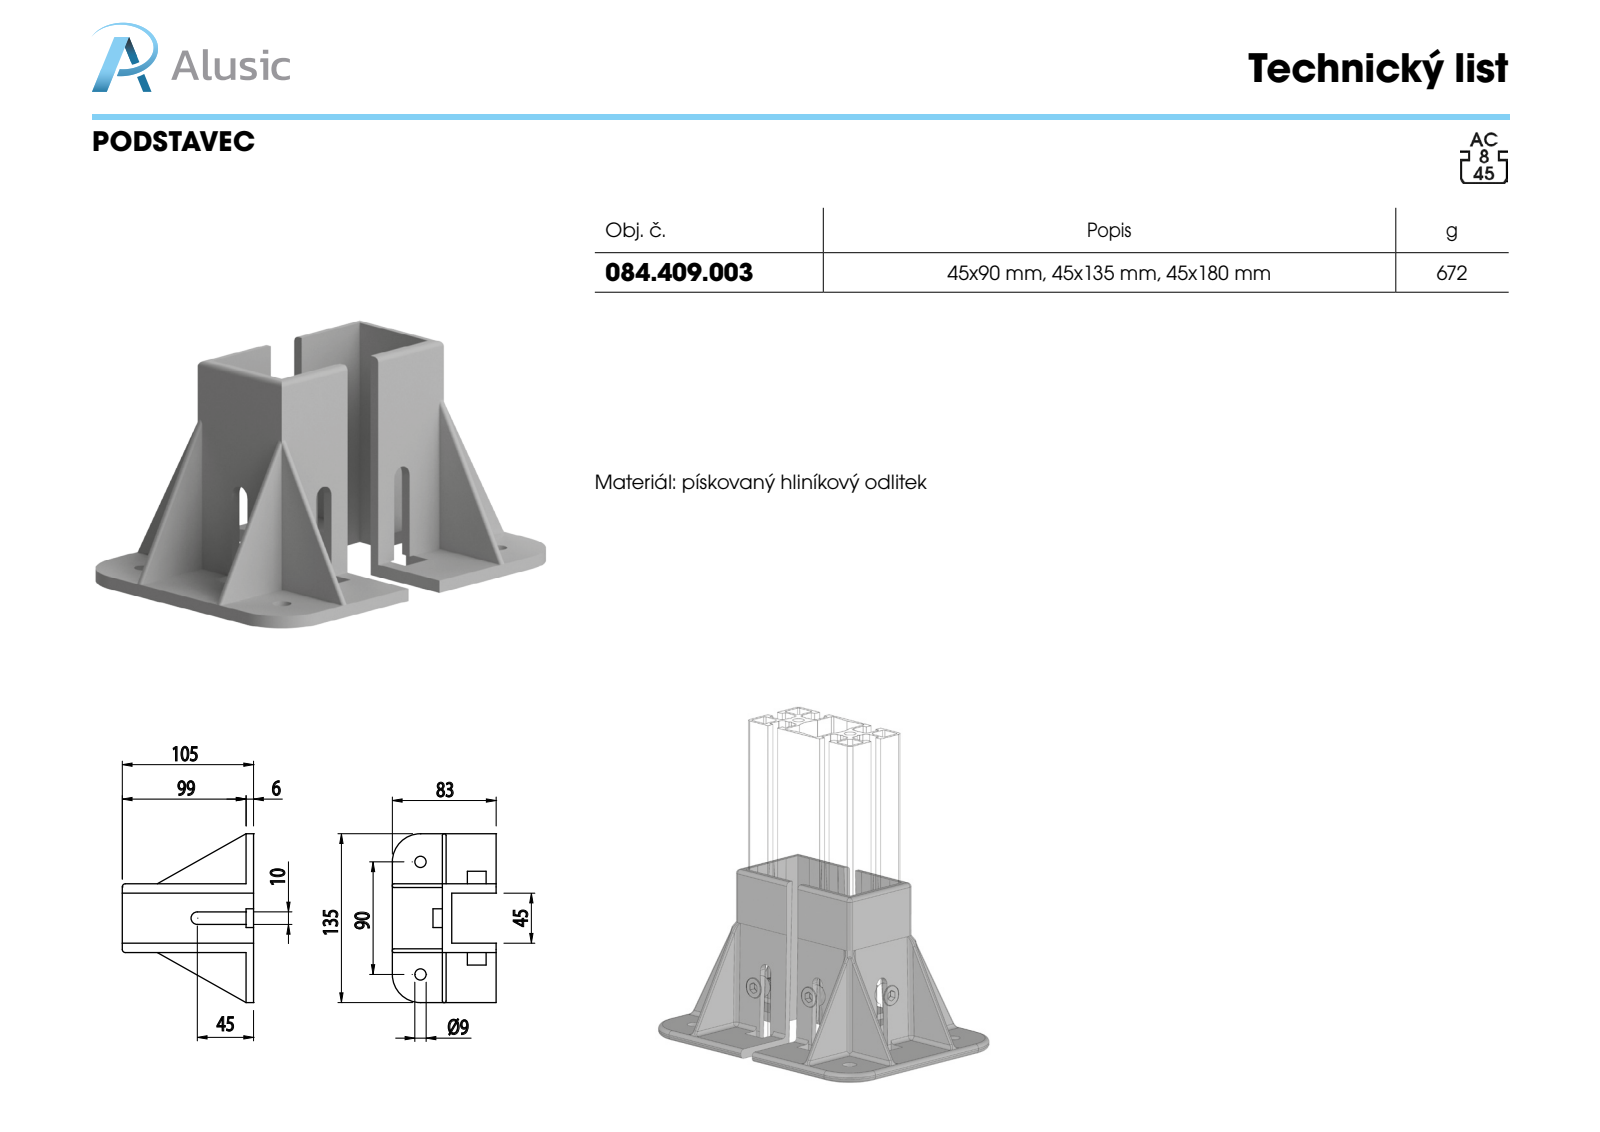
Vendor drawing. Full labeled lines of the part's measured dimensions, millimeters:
Part name (STEP PRODUCT): 084.409.003
STEP written by: SolidWorks 2011 (CONFIG_CONTROL_DESIGN)
Units: millimetres
Bodies: 1 solid, 71 faces (51 planar, 20 cylindrical, 0 other)
Overall size (bounding box): 135 × 105 × 83
Volume: 125 913 mm³ · Surface area: 57 365 mm²
Round holes (diameter × count): ⌀9 ×2
Partial cylindrical surfaces — rounded edges, fillets, slot ends (radius × count): R1.2 ×8, R2.5 ×3, R5 ×2, R22.5 ×2
Main face-to-face distances: 5, 6, 50, 3, 2, 45, 55, 40, 43, 52
Hole centre spacings: 90
